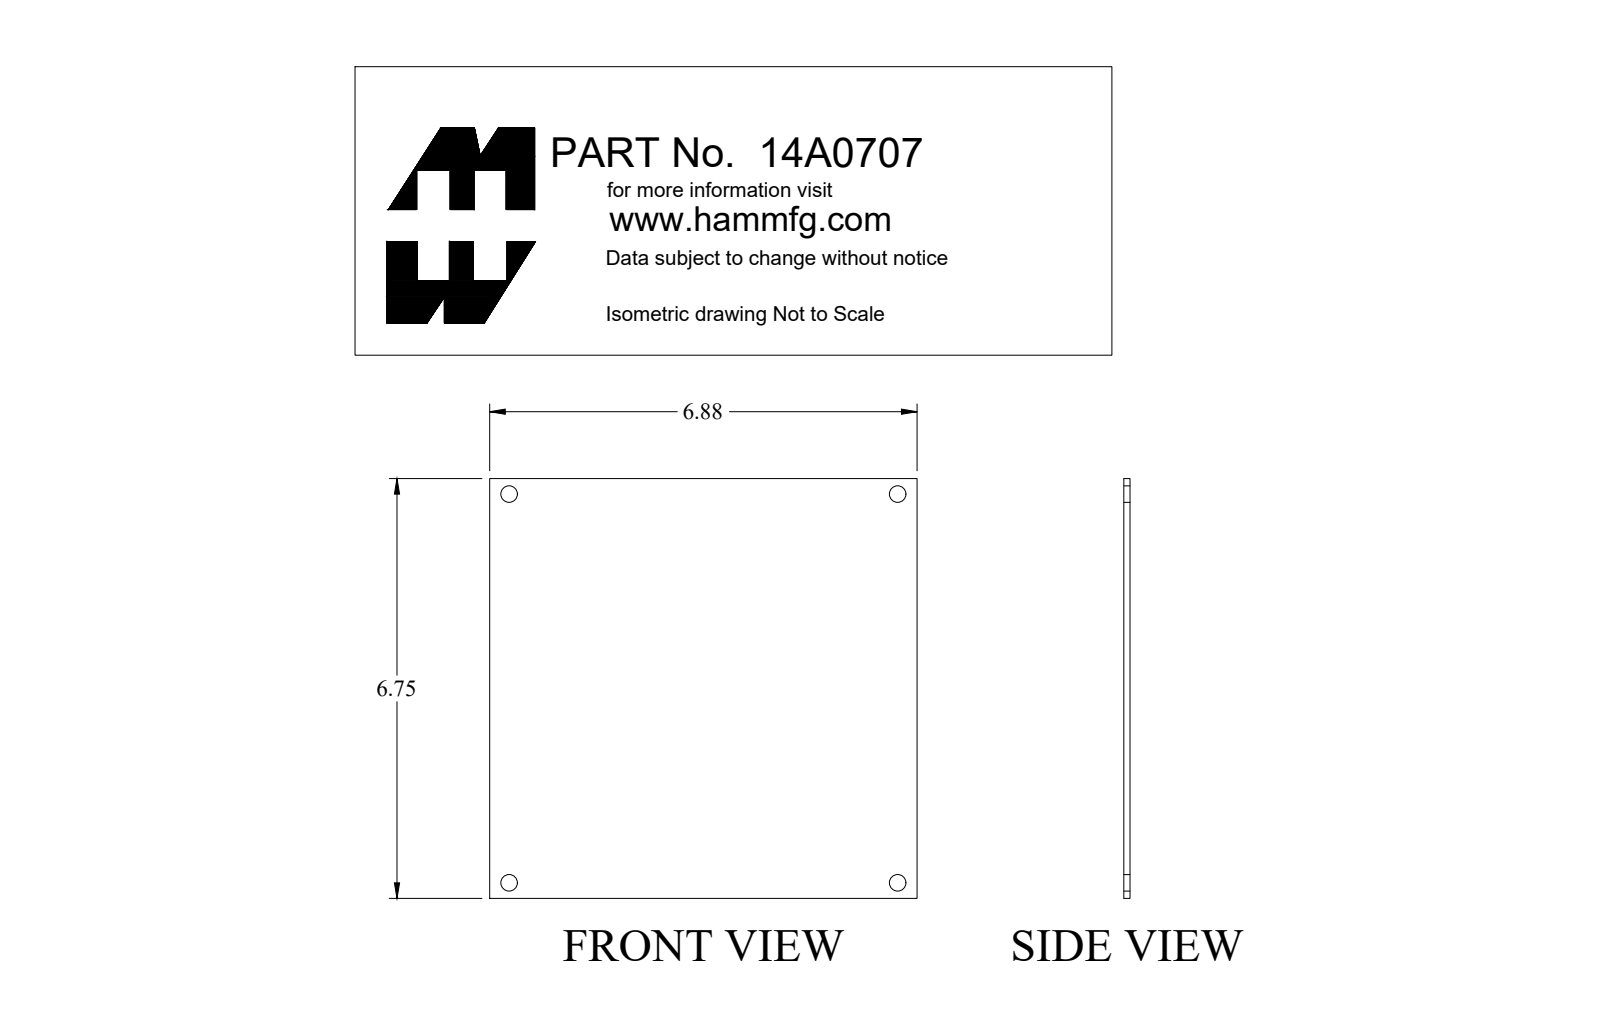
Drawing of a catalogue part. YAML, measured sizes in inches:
part_name: "14A0707"
step_written_by: "SolidWorks 2018 (AUTOMOTIVE_DESIGN)"
units: inches
bodies: {solids: 1, faces: 10, planar: 6, cylindrical: 4, other: 0}
overall_size: [6.875, 6.75, 0.1]
volume: 4.619
surface_area: 95.43
round_holes:
  - {diameter: 0.265, count: 4}
face_to_face_distances: [0.1, 6.75, 6.875]
hole_center_spacings: [6.25, 6.251, 8.84]
